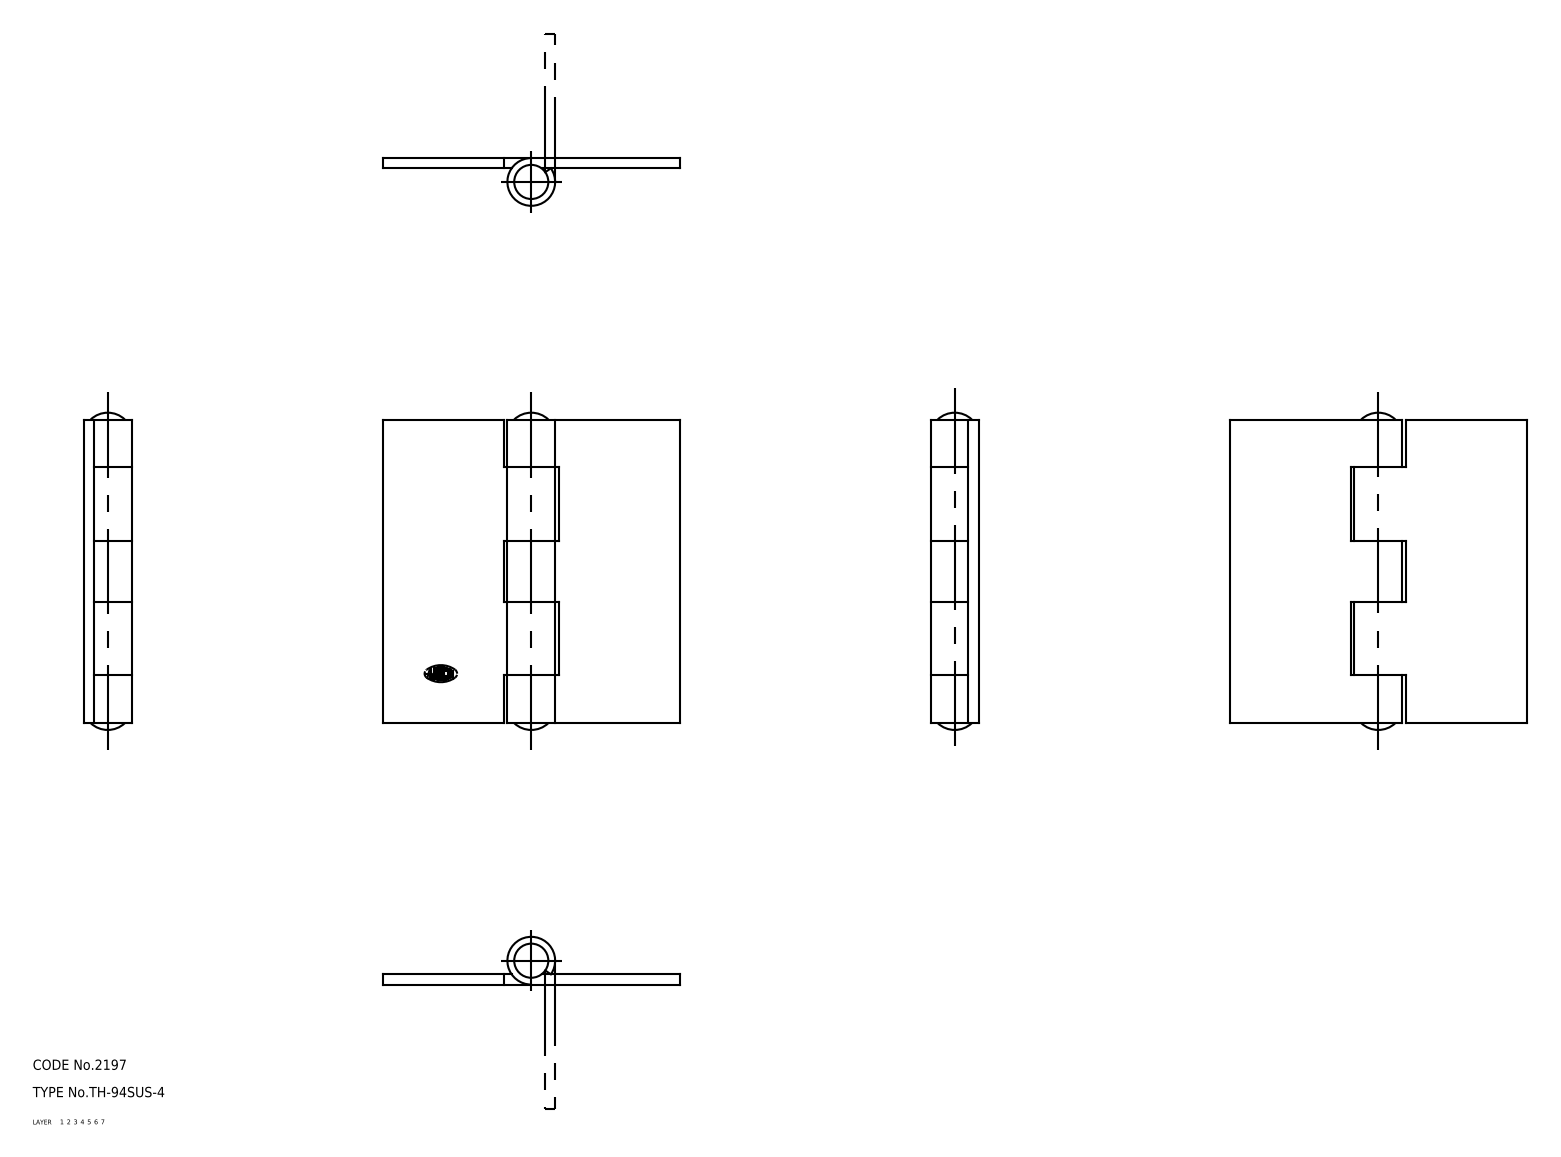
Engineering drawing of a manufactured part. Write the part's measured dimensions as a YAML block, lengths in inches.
part_name: "hinge piece_B; hinge piece_A; shaft; TH_94SUS_4_19391_36"
step_written_by: "CADfix (AUTOMOTIVE_DESIGN)"
units: inches
bodies: {solids: 3, faces: 44, planar: 0, cylindrical: 0, other: 44}
overall_size: [3.661, 3.425, 0.551]
volume: 2.047
surface_area: 37.74
